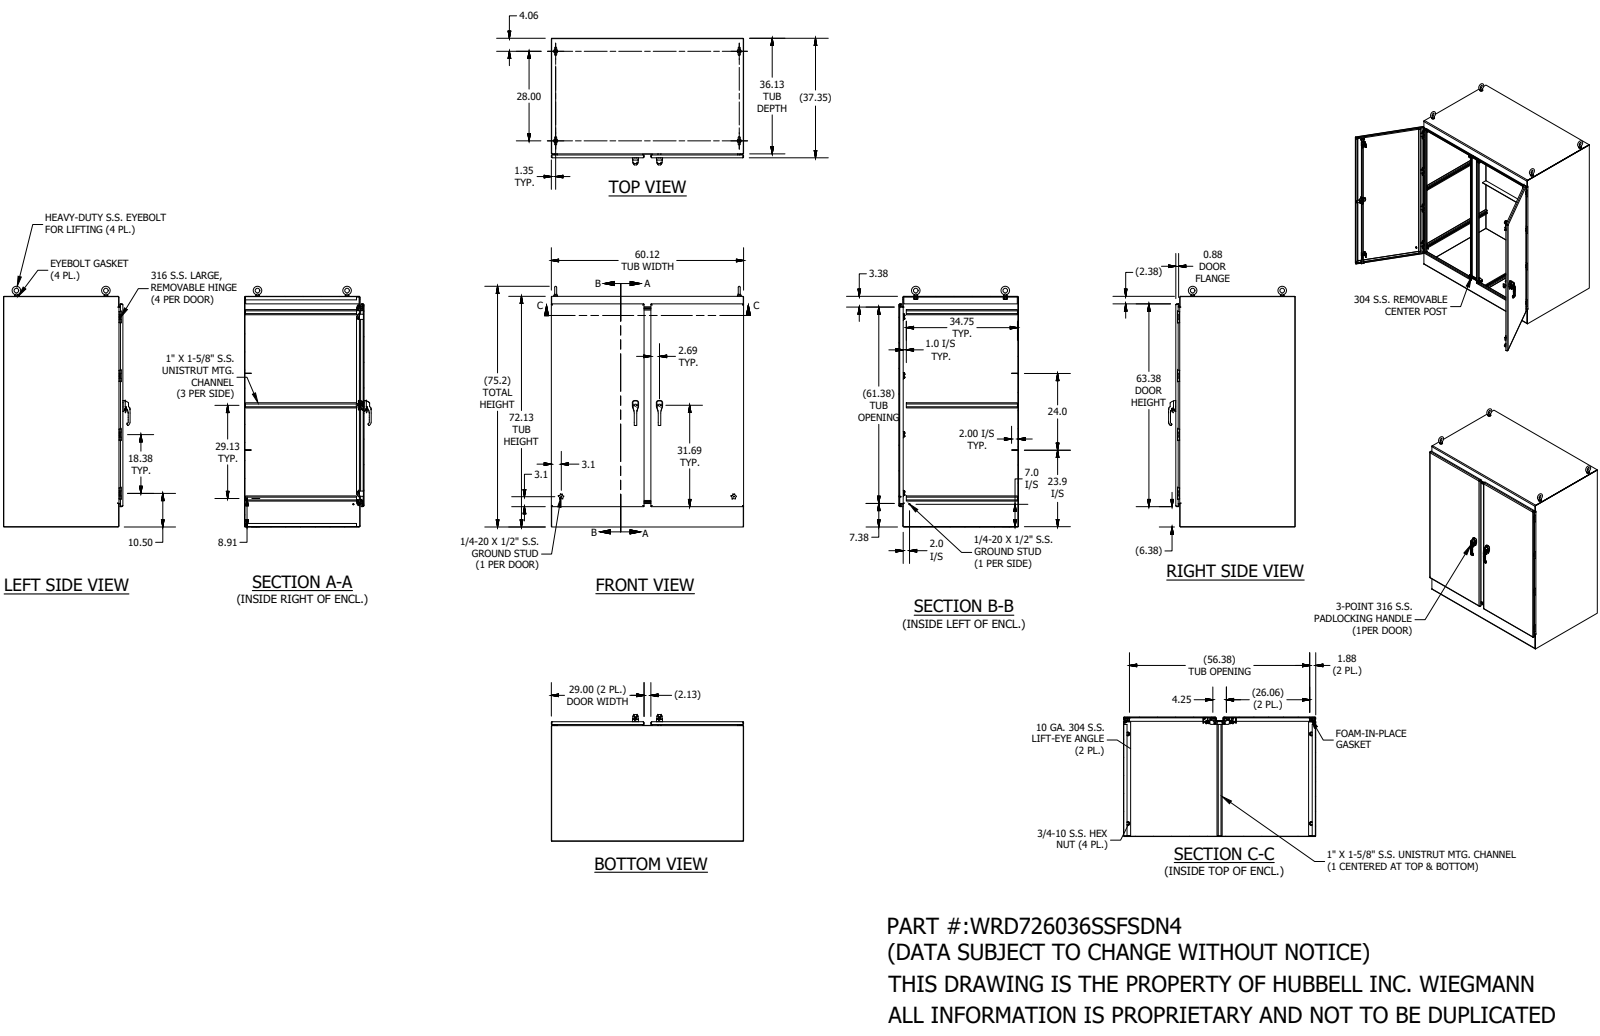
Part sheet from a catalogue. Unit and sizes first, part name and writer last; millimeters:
Units: millimetres
Overall size (bounding box): 1911.3 × 1527.4 × 1005.8
Round holes (diameter × count): ⌀3.6 ×48, ⌀6.8 ×20, ⌀5 ×16, ⌀7.5 ×16, ⌀16.5 ×16, ⌀3.5 ×8, ⌀4.2 ×8, ⌀4.7 ×8, ⌀5.1 ×8, ⌀6.7 ×8, ⌀5.4 ×6, ⌀7.1 ×6
Round bosses / shafts (diameter × count): ⌀6.4 ×33, ⌀15.9 ×16, ⌀4.6 ×16, ⌀6 ×8, ⌀6 ×6, ⌀31.8 ×4, ⌀28.4 ×4, ⌀25.4 ×4
Partial cylindrical surfaces — rounded edges, fillets, slot ends (radius × count): R0.5 ×344, R0.3 ×229, R1.6 ×64, R3.2 ×58, R0.5 ×42, R2 ×28, R1.3 ×26, R1 ×22
Main face-to-face distances: 2.6, 1524.5, 1829.3, 946, 943.4, 2.6, 948.7, 946, 1521.9, 1527.2
Hole centre spacings: 224.6, 0.5, 1566.6, 0.6, 25.4, 221.5, 221.8, 466.7
Volume: 39 310 000 mm³ · Surface area: 28 770 000 mm²
Bodies: 235 solids, 9338 faces (3918 planar, 3266 cylindrical, 2154 other)
Part name (STEP PRODUCT): WRD726036SSFSDN4; WRD7260SSFSDN4FB; WRD7236SSFSDN4RS; WRD7236SSFSDN4LS (+8 more)
STEP written by: Autodesk Inventor 2018 (AUTOMOTIVE_DESIGN)
